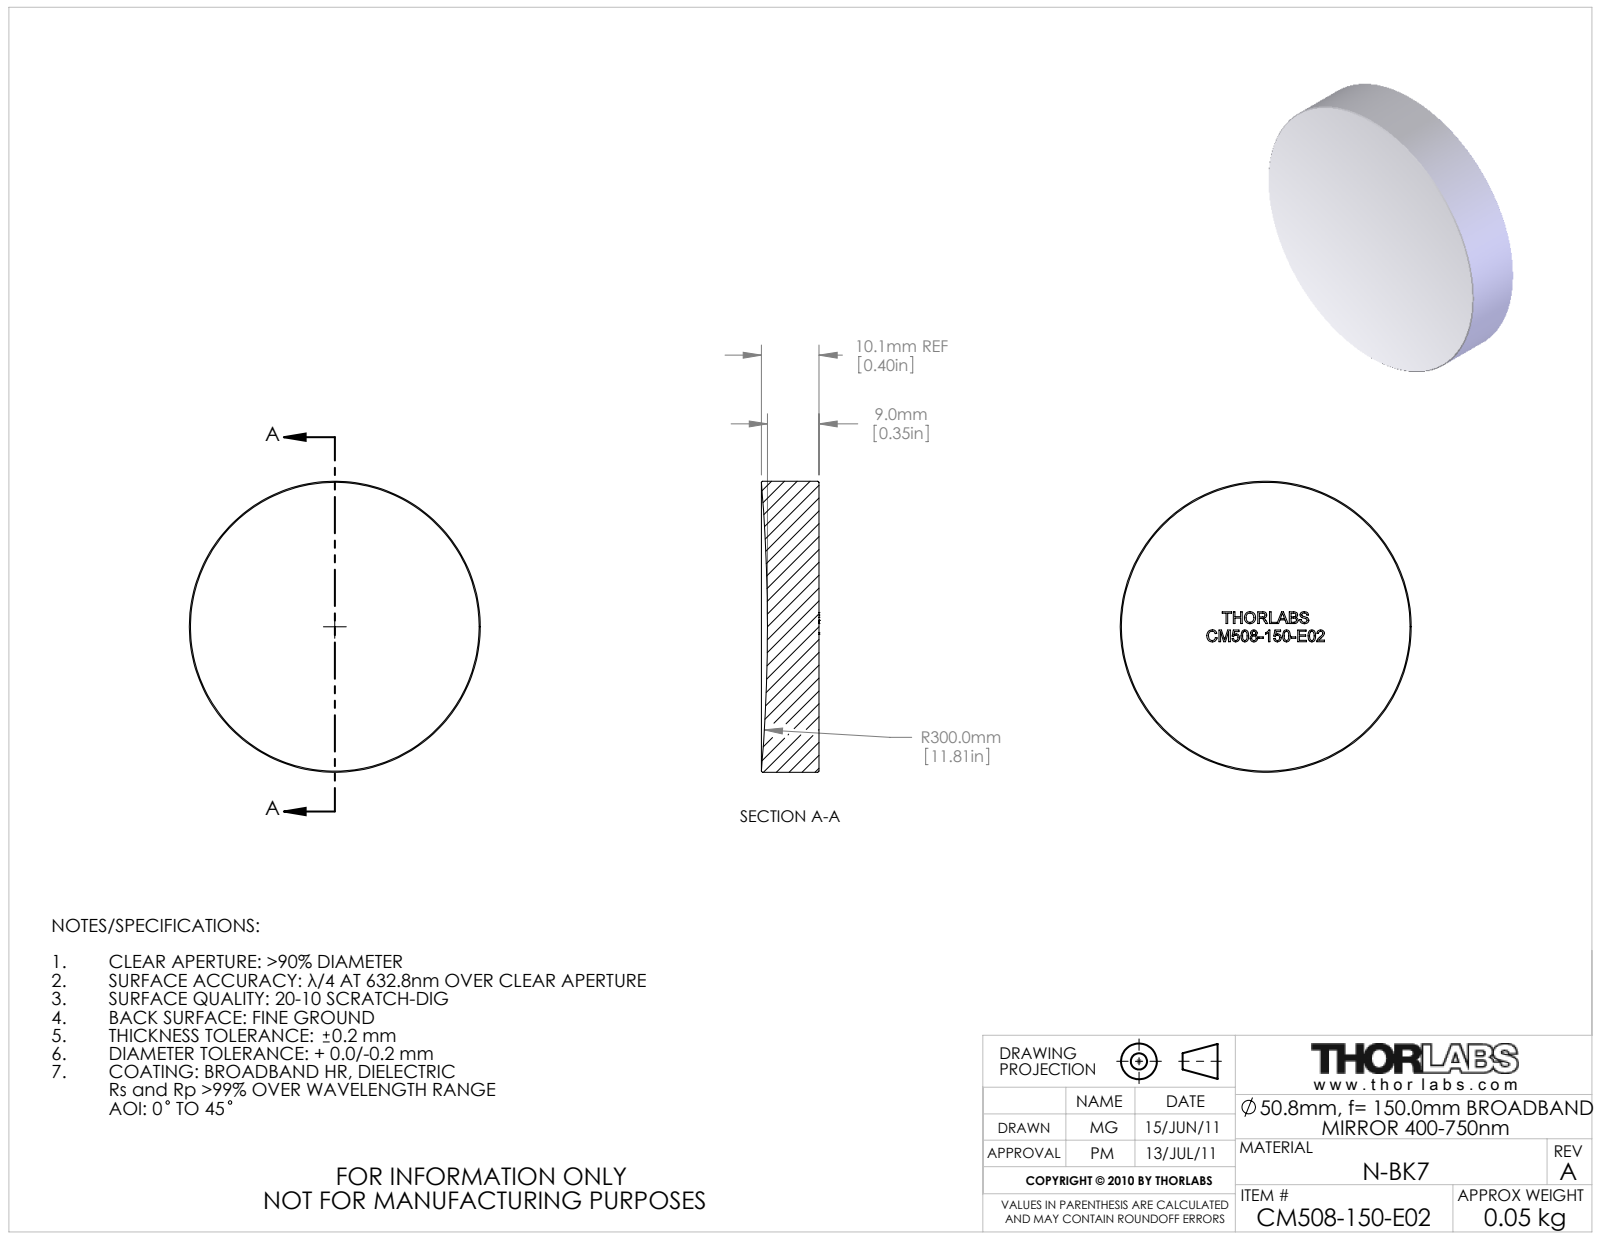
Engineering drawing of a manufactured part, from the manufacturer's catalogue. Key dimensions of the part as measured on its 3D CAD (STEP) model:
Part name (STEP PRODUCT): 22632-E0W
STEP written by: SolidWorks 2011 (AUTOMOTIVE_DESIGN)
Units: millimetres
Bodies: 0 solids, 44 faces (34 planar, 2 cylindrical, 8 other)
Overall size (bounding box): 50.8 × 50.8 × 10.06
Round bosses / shafts (diameter × count): ⌀50.8 ×1
